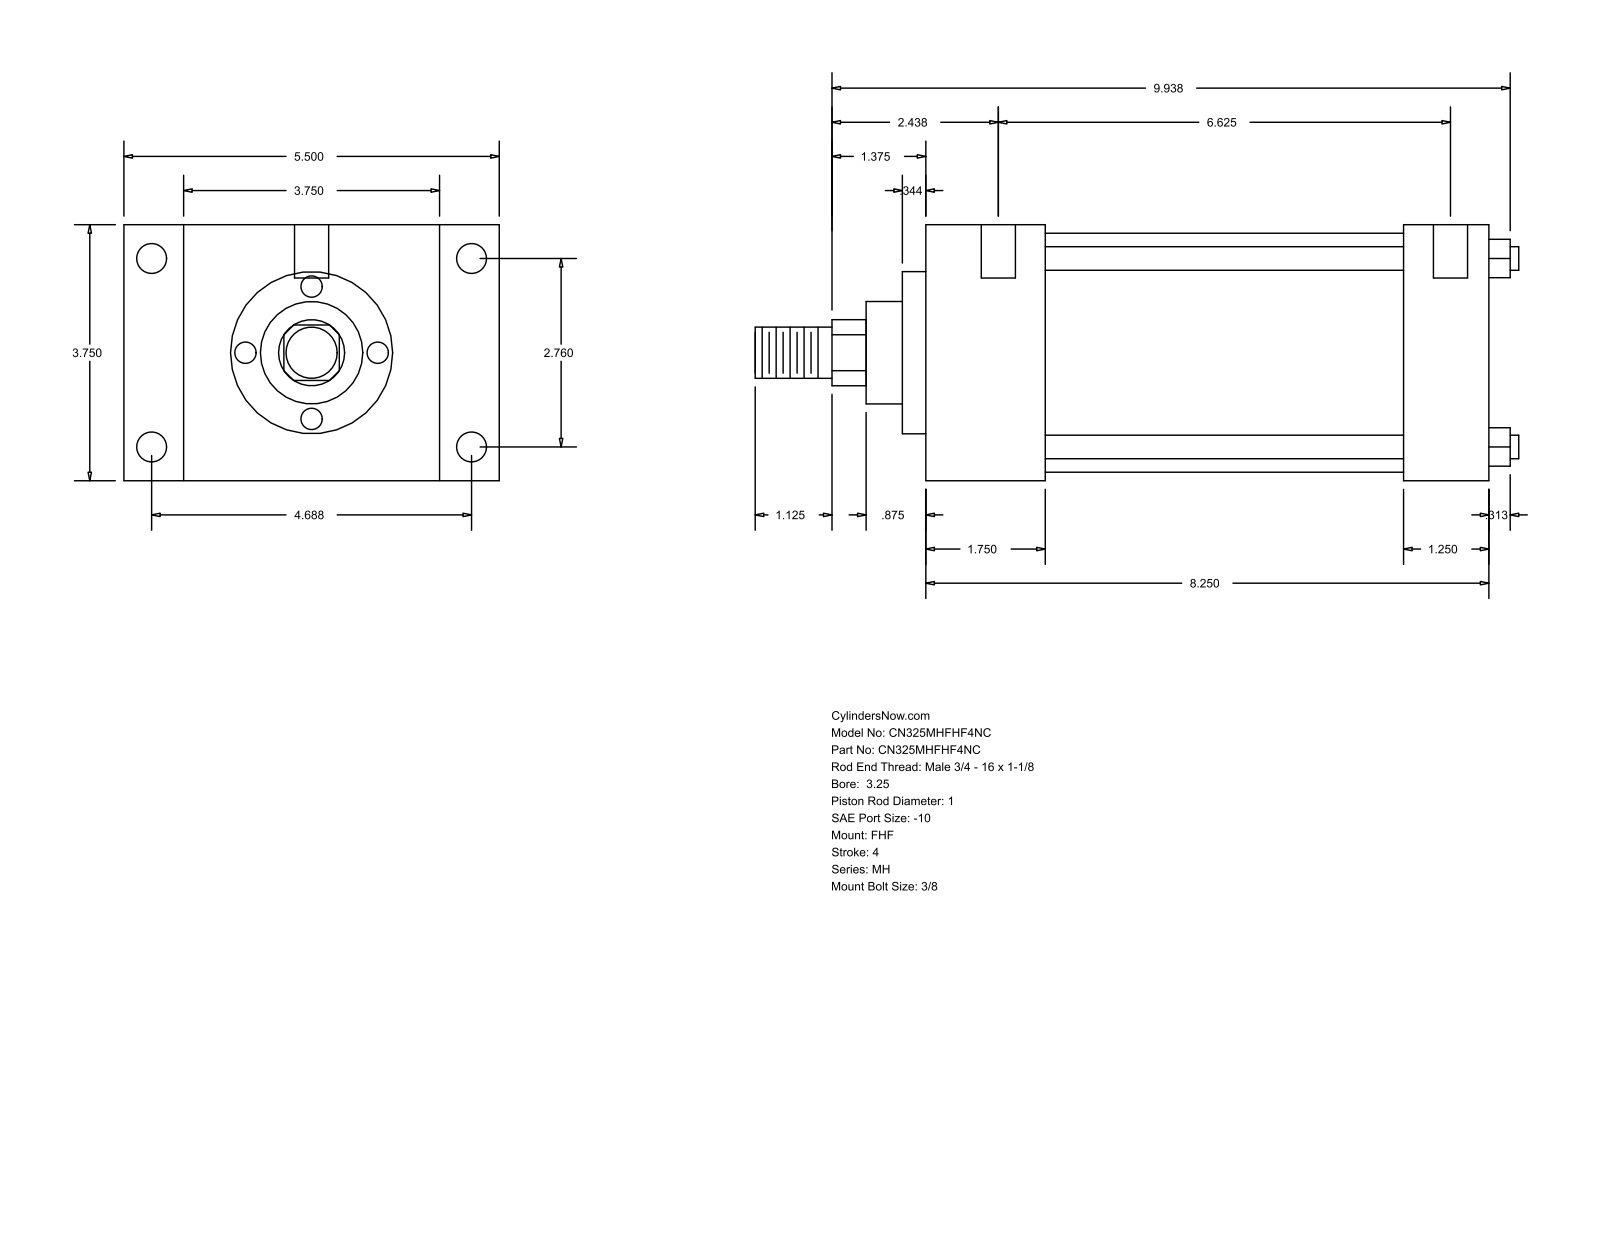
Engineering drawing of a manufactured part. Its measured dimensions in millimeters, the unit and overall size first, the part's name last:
Units: millimetres
Overall size (bounding box): 284.16 × 139.7 × 95.25
Round holes (diameter × count): ⌀5.56 ×4, ⌀11.13 ×4, ⌀12.7 ×2
Round bosses / shafts (diameter × count): ⌀8.76 ×4, ⌀88.9 ×1, ⌀60.33 ×1, ⌀38.1 ×1, ⌀25.4 ×1, ⌀19.05 ×1
Partial cylindrical surfaces — rounded edges, fillets, slot ends (radius × count): R12.29 ×1
Main face-to-face distances: 95.24, 209.55, 44.46, 165.09, 22.23, 117.47, 139.7, 177.8, 133.34, 31.75
Hole centre spacings: 70.1, 119.06, 138.16, 174.62, 1.58, 4.76, 168.28, 169.86
Bodies: 0 solids, 90 faces (61 planar, 29 cylindrical, 0 other)
Part name (STEP PRODUCT): MH_FHF__0325_1
STEP written by: GSSL Pune (CONFIG_CONTROL_DESIGN)
